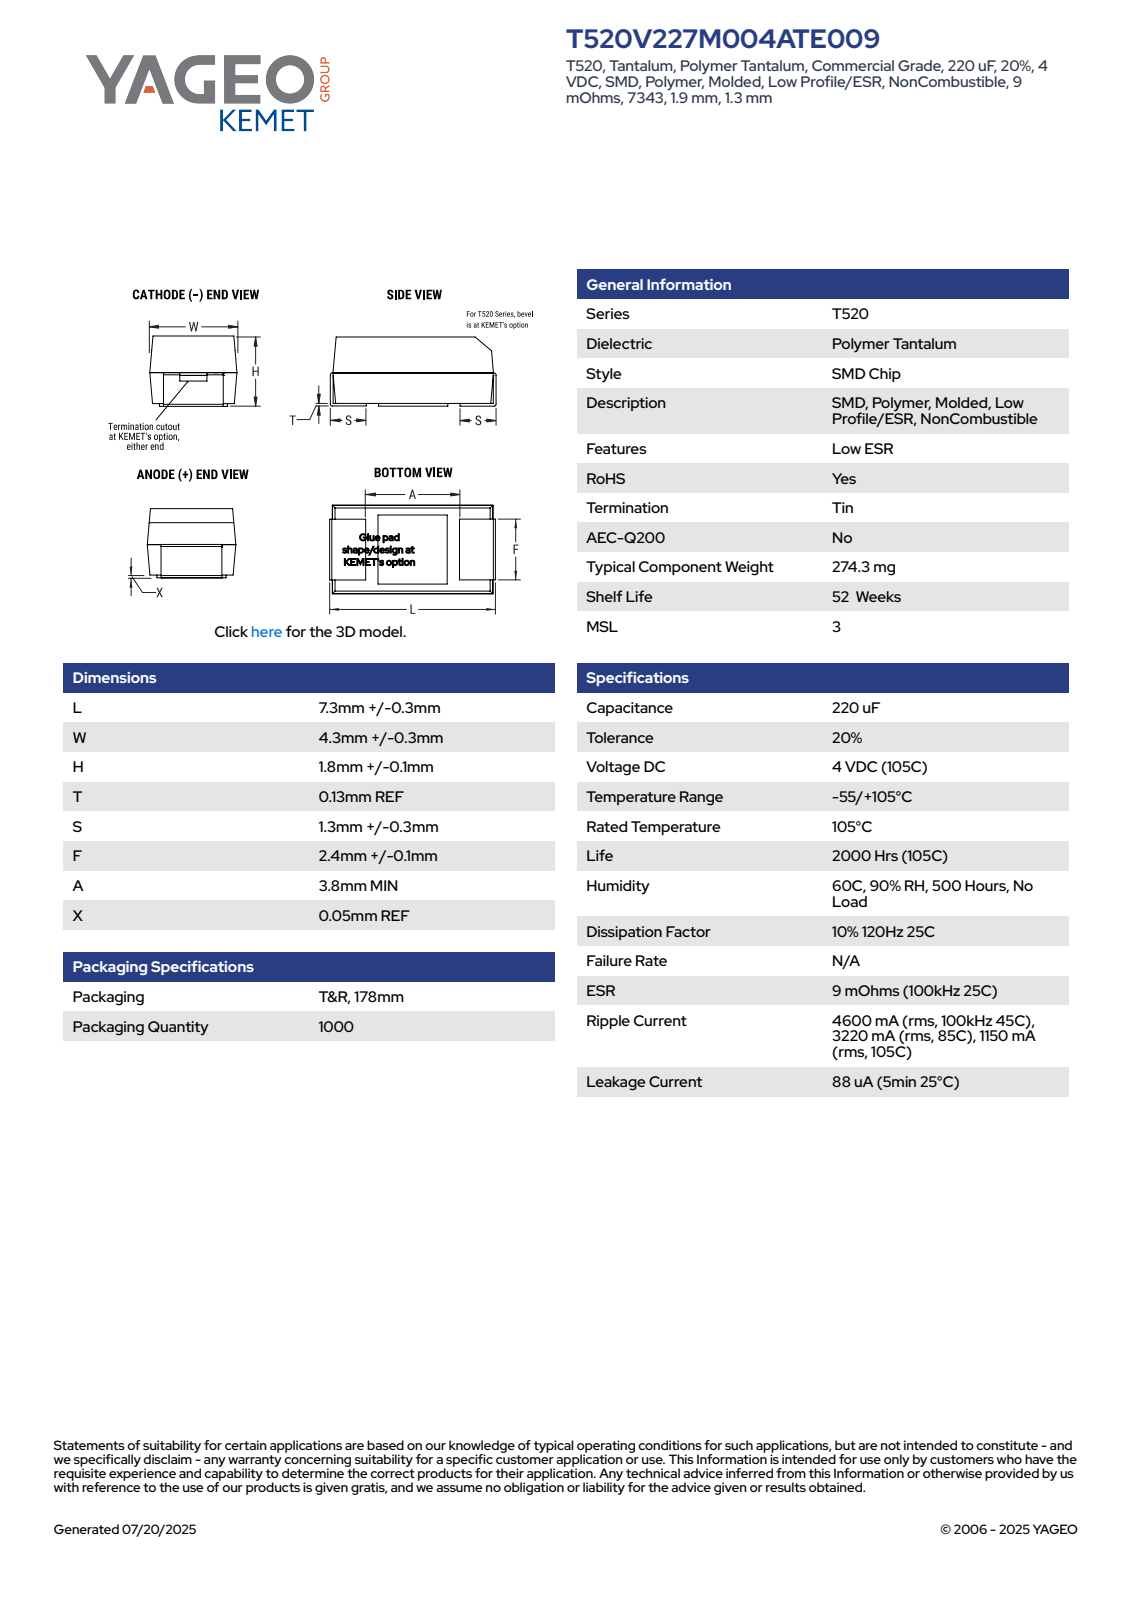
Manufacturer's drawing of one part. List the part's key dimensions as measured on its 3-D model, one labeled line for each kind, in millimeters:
Part name (STEP PRODUCT): CTS_TCM2NOBNOKBOPT_7343_L7.6W4.6H1.9T0.13S1.3F2.5A3.6X0.05
STEP written by: SolidWorks 2014 (AUTOMOTIVE_DESIGN)
Units: millimetres
Bodies: 4 solids, 90 faces (86 planar, 4 cylindrical, 0 other)
Overall size (bounding box): 7.6 × 4.6 × 1.91
Volume: 58 mm³ · Surface area: 118 mm²
Partial cylindrical surfaces — rounded edges, fillets, slot ends (radius × count): R0.13 ×4
Main face-to-face distances: 1.82, 4.53, 1.77, 7.15, 1.9, 7.47, 7.34, 7.6, 1.17, 1.3
